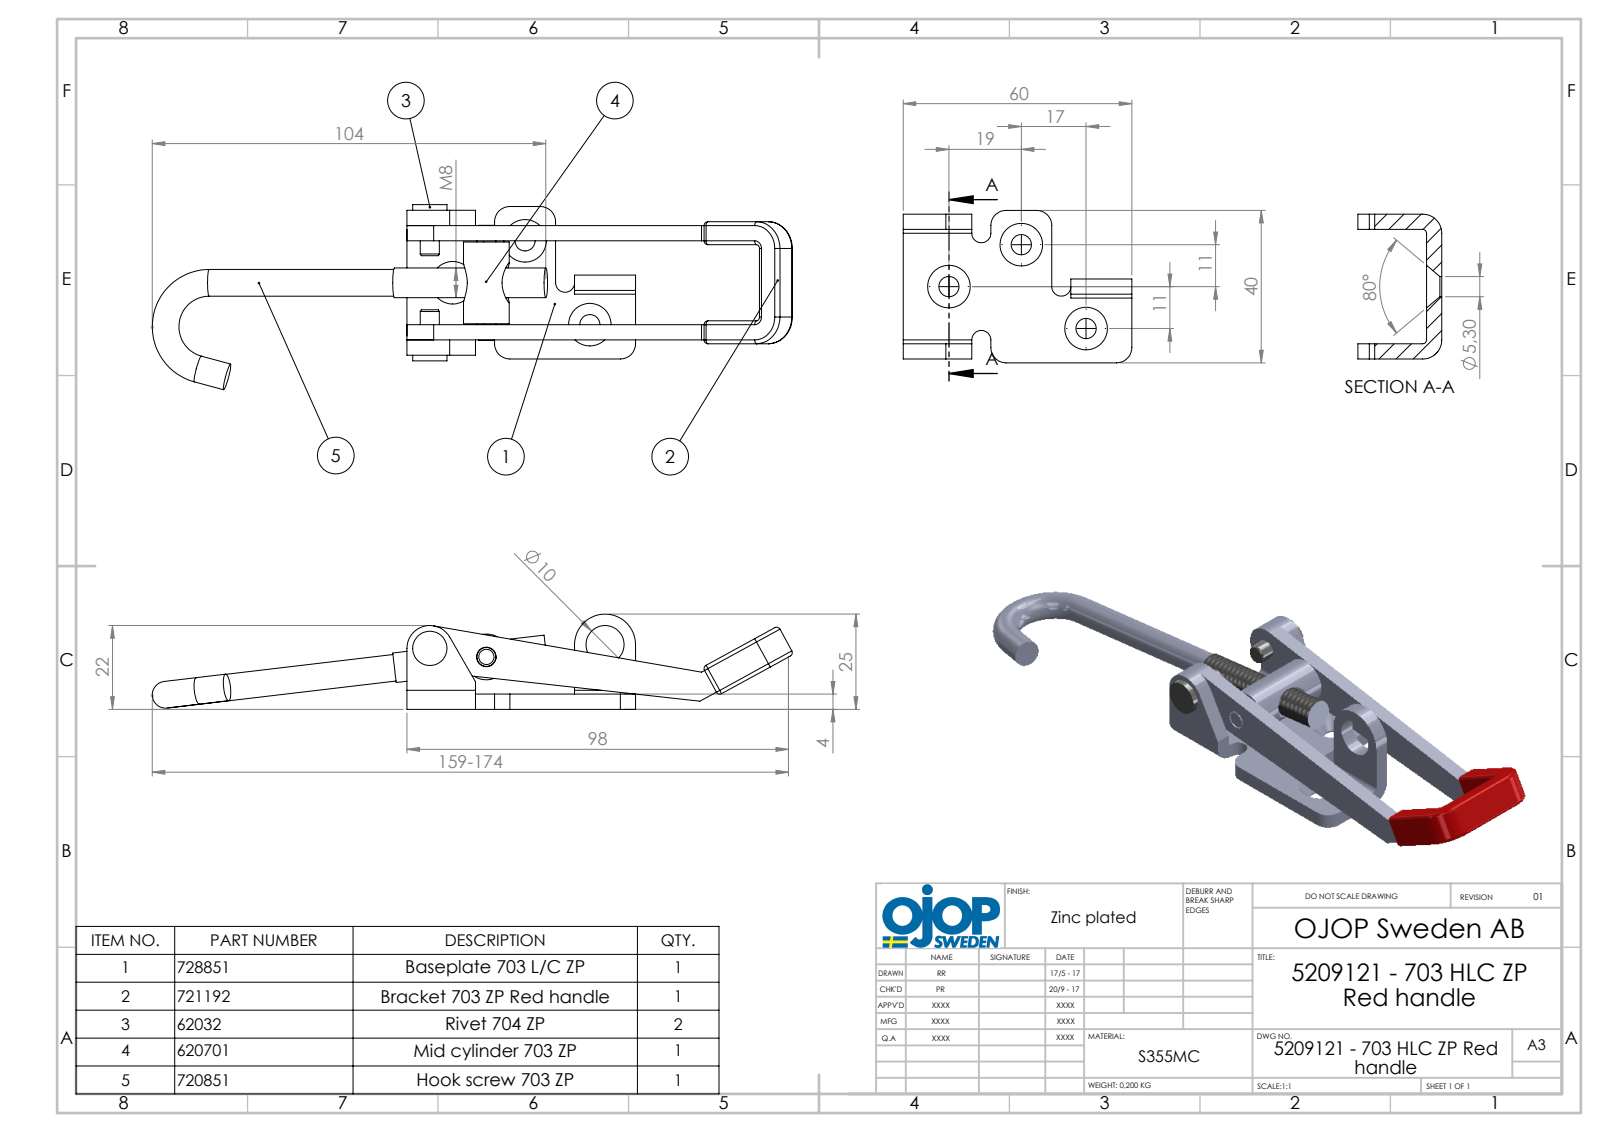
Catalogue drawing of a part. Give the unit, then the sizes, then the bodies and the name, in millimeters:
Units: millimetres
Overall size (bounding box): 167.87 × 48.06 × 25.11
Round holes (diameter × count): ⌀5.3 ×3, ⌀5.1 ×2, ⌀7.2 ×1, ⌀7.7 ×1, ⌀10 ×1
Round bosses / shafts (diameter × count): ⌀7 ×3, ⌀5 ×2, ⌀12 ×1, ⌀9 ×1, ⌀7.8 ×1
Partial cylindrical surfaces — rounded edges, fillets, slot ends (radius × count): R1 ×21, R4 ×4, R2.5 ×3, R5 ×3, R0.75 ×2, R7.25 ×2, R6 ×1, R8 ×1
Main face-to-face distances: 4, 26.7, 30.7, 17, 22.7, 13, 9, 21, 1.25, 5.25
Hole centre spacings: 15.02, 21.95, 27.8, 31.2, 37.64, 46.01
Volume: 26 856 mm³ · Surface area: 17 940 mm²
Bodies: 6 solids, 195 faces (67 planar, 92 cylindrical, 36 other)
Part name (STEP PRODUCT): 704 - Rivet Gradin; 703 -bygelrödplast; 703- Platta LC; 5209121 - HLC fzb skruvhake röd (+2 more)
STEP written by: SolidWorks 2015 (AUTOMOTIVE_DESIGN)
